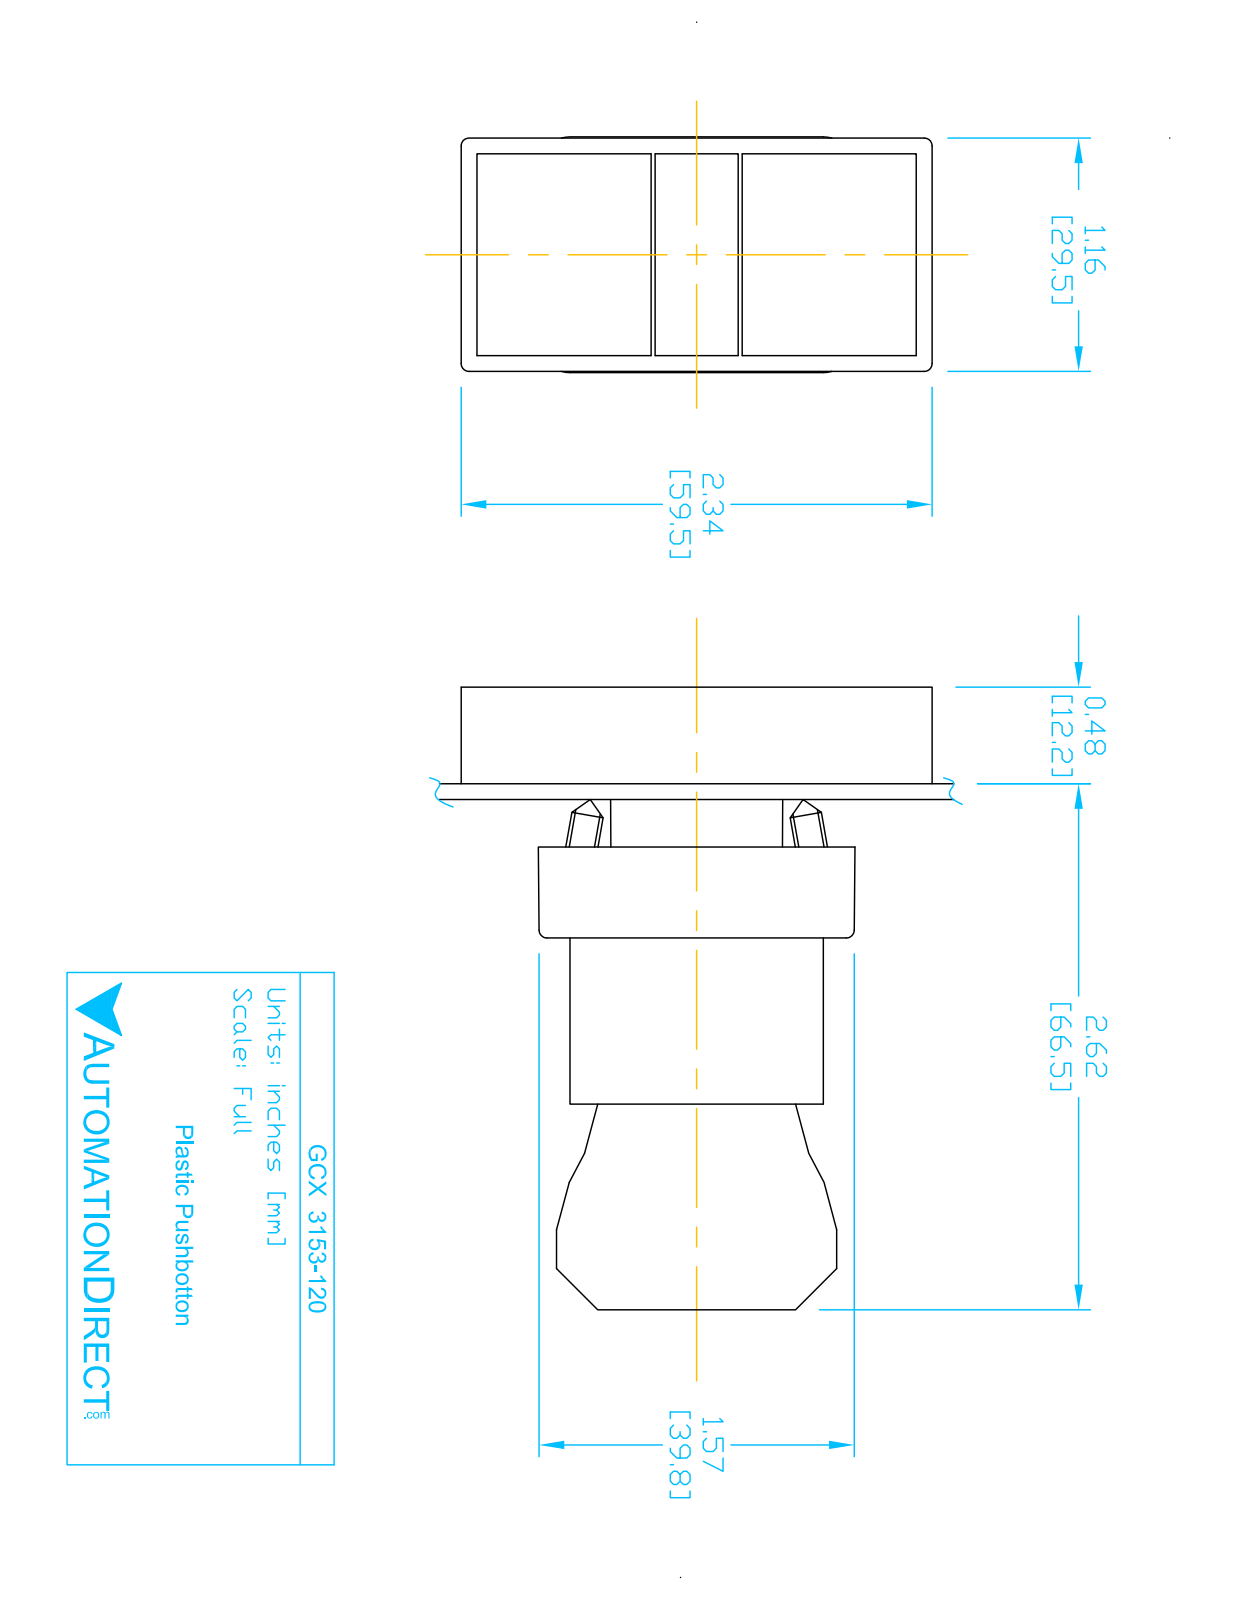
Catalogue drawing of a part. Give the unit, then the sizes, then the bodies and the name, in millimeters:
Units: millimetres
Overall size (bounding box): 77.3 × 59.5 × 29.9
Round holes (diameter × count): ⌀2 ×4, ⌀2.2 ×2, ⌀3.1 ×2, ⌀3.3 ×2, ⌀5 ×1, ⌀11.9 ×1, ⌀18 ×1, ⌀22.3 ×1, ⌀22.6 ×1
Round bosses / shafts (diameter × count): ⌀4 ×4, ⌀24 ×1, ⌀21.7 ×1, ⌀19.8 ×1, ⌀15 ×1, ⌀12.8 ×1
Partial cylindrical surfaces — rounded edges, fillets, slot ends (radius × count): R1.5 ×24, R1 ×12, R3.1 ×12, R4 ×12, R1 ×8, R1.6 ×2, R2 ×2, R3.3 ×2
Main face-to-face distances: 1, 0.5, 1.5, 14.7, 15.1, 18.8, 30.3, 11.5, 21, 39.8
Hole centre spacings: 6, 25.5, 24.7, 12, 13.7, 13.8, 27.5, 12.3
Volume: 70 100 mm³ · Surface area: 36 050 mm²
Bodies: 9 solids, 542 faces (355 planar, 156 cylindrical, 31 other)
Part name (STEP PRODUCT): ecx1040; ECX1050; GCX3153-120 OPERATOR; ECX3029-2 (+2 more)
STEP written by: SolidWorks 2016 (AUTOMOTIVE_DESIGN)
